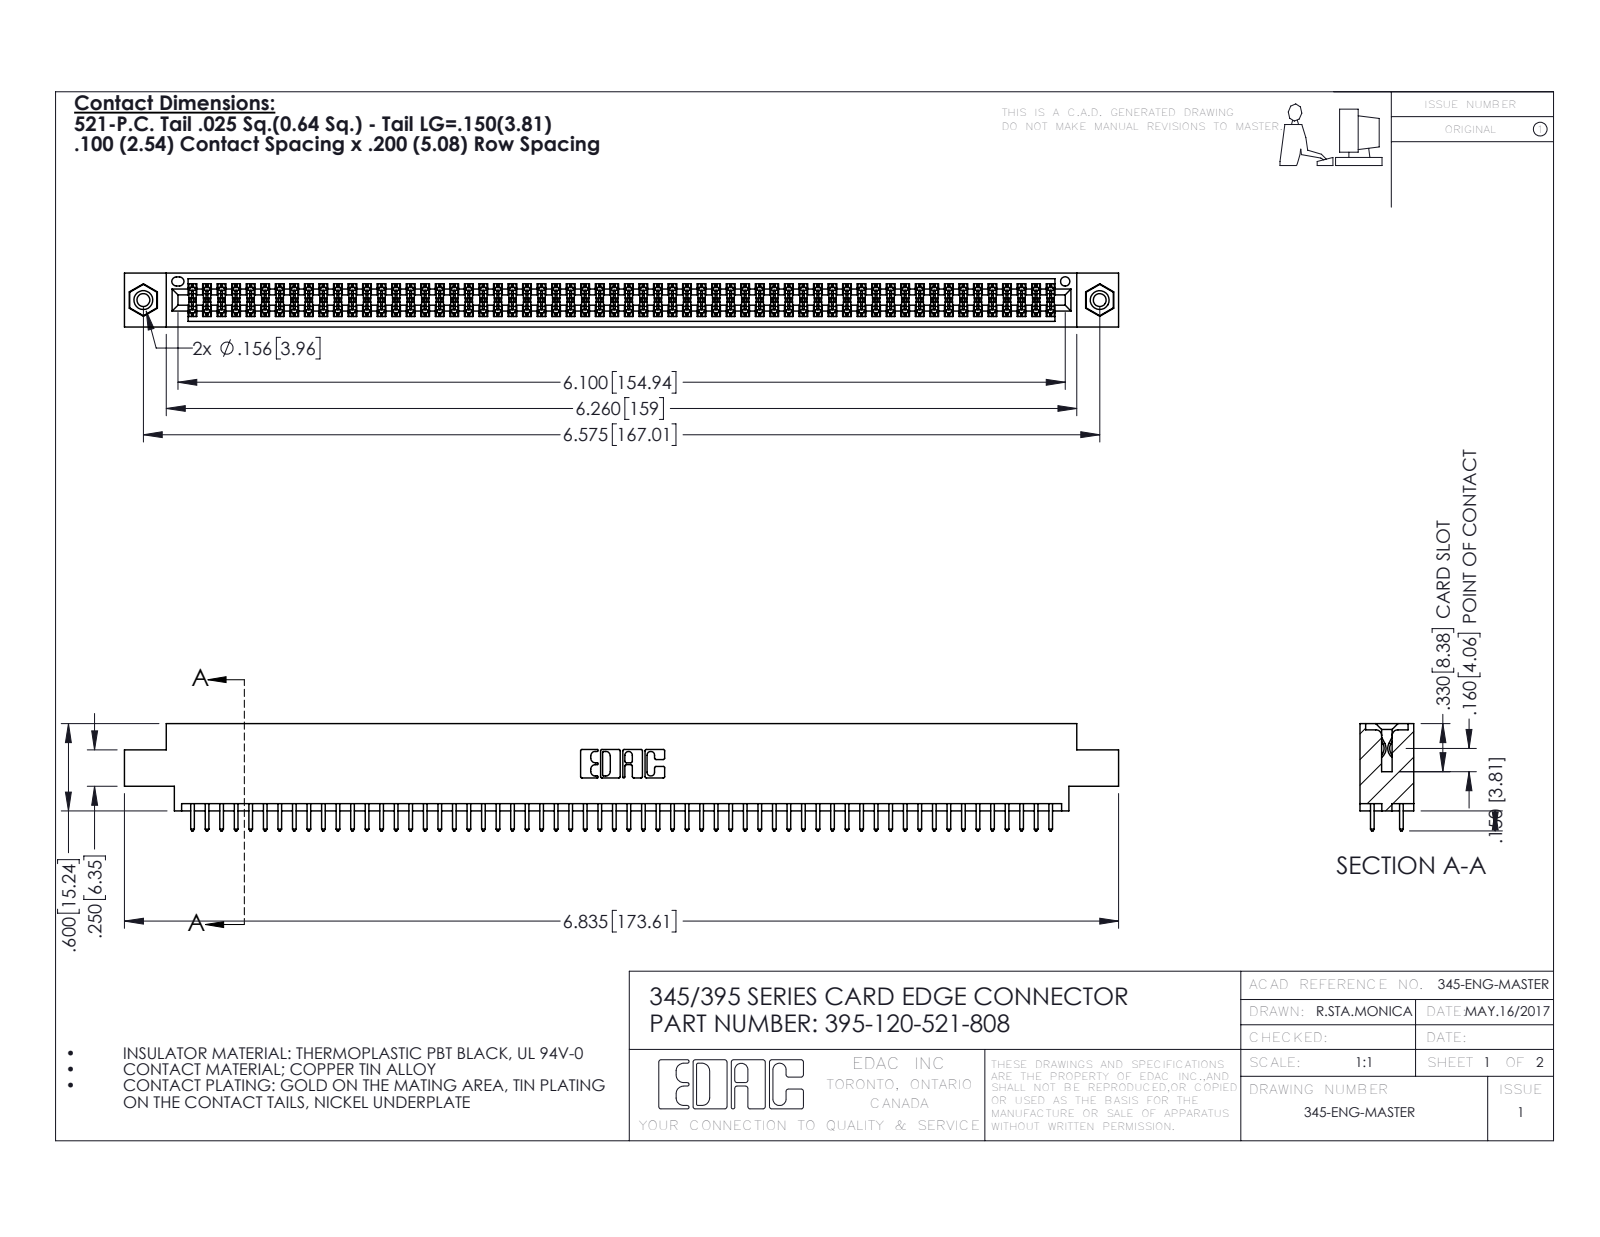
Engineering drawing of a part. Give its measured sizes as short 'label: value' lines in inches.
name: 345 Part_0.170 Offset - 0.156 Dia-TI; 345-250-001_345-250-003-102; 395-120-521-808; 345-292-001_345-293-121
written by: SolidWorks 2016 (CONFIG_CONTROL_DESIGN)
unit: in
bodies: 123 solids, 6190 faces (4076 planar, 2098 cylindrical, 16 other)
size: 6.835 × 0.737 × 0.37
volume: 1.029 in³; area: 38.92 in²
holes: 2× ⌀0.089, 2× ⌀0.125, 2× ⌀0.156, 1× ⌀0.064
bosses: 2× ⌀0.155
rounds: 180× R0.006, 120× R0.01, 22× R0.01, 6× R0.007, 6× R0.031, 3× R0.026, 2× R0.014, 2× R0.019
face distances: 0.072, 0.298, 0.2, 0.37, 0.098, 0.272, 0.025, 0.225, 0.175, 0.149
hole spacings: 0.27, 6.339, 6.575
